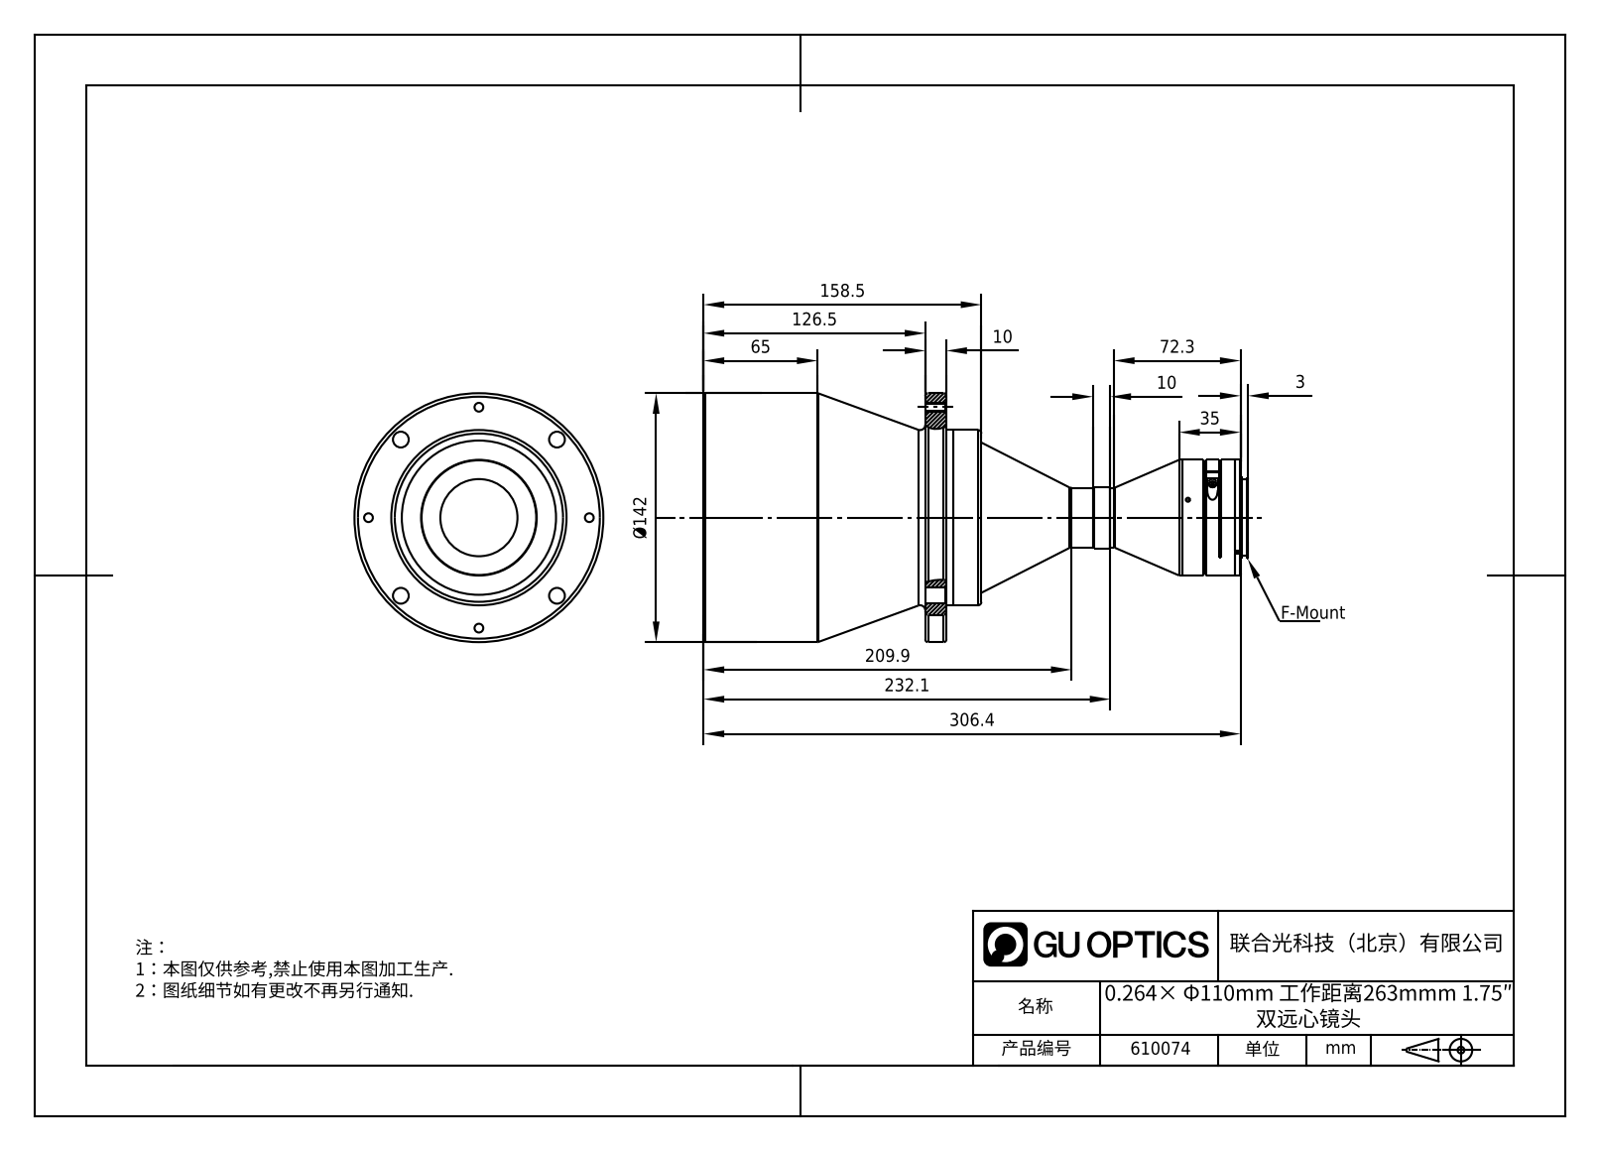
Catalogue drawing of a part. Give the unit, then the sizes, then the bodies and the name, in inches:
Units: inches
Overall size (bounding box): 12.181 × 5.591 × 5.591
Round holes (diameter × count): ⌀0.197 ×4, ⌀0.354 ×4
Round bosses / shafts (diameter × count): ⌀5.591 ×1, ⌀3.937 ×1, ⌀2.598 ×1, ⌀1.732 ×1, ⌀1.378 ×1, ⌀1.339 ×1
Main face-to-face distances: 5.453, 4.98, 0.472, 12.063, 7.083, 6.61, 12.181, 7.201, 6.728, 0.118
Hole centre spacings: 1.898, 3.508, 4.583, 4.961, 4.961
Volume: 148.8 in³ · Surface area: 200.3 in²
Bodies: 1 solid, 62 faces (8 planar, 32 cylindrical, 22 other)
Part name (STEP PRODUCT): DTCM175-110-AL
STEP written by: SolidWorks 2017 (CONFIG_CONTROL_DESIGN)
